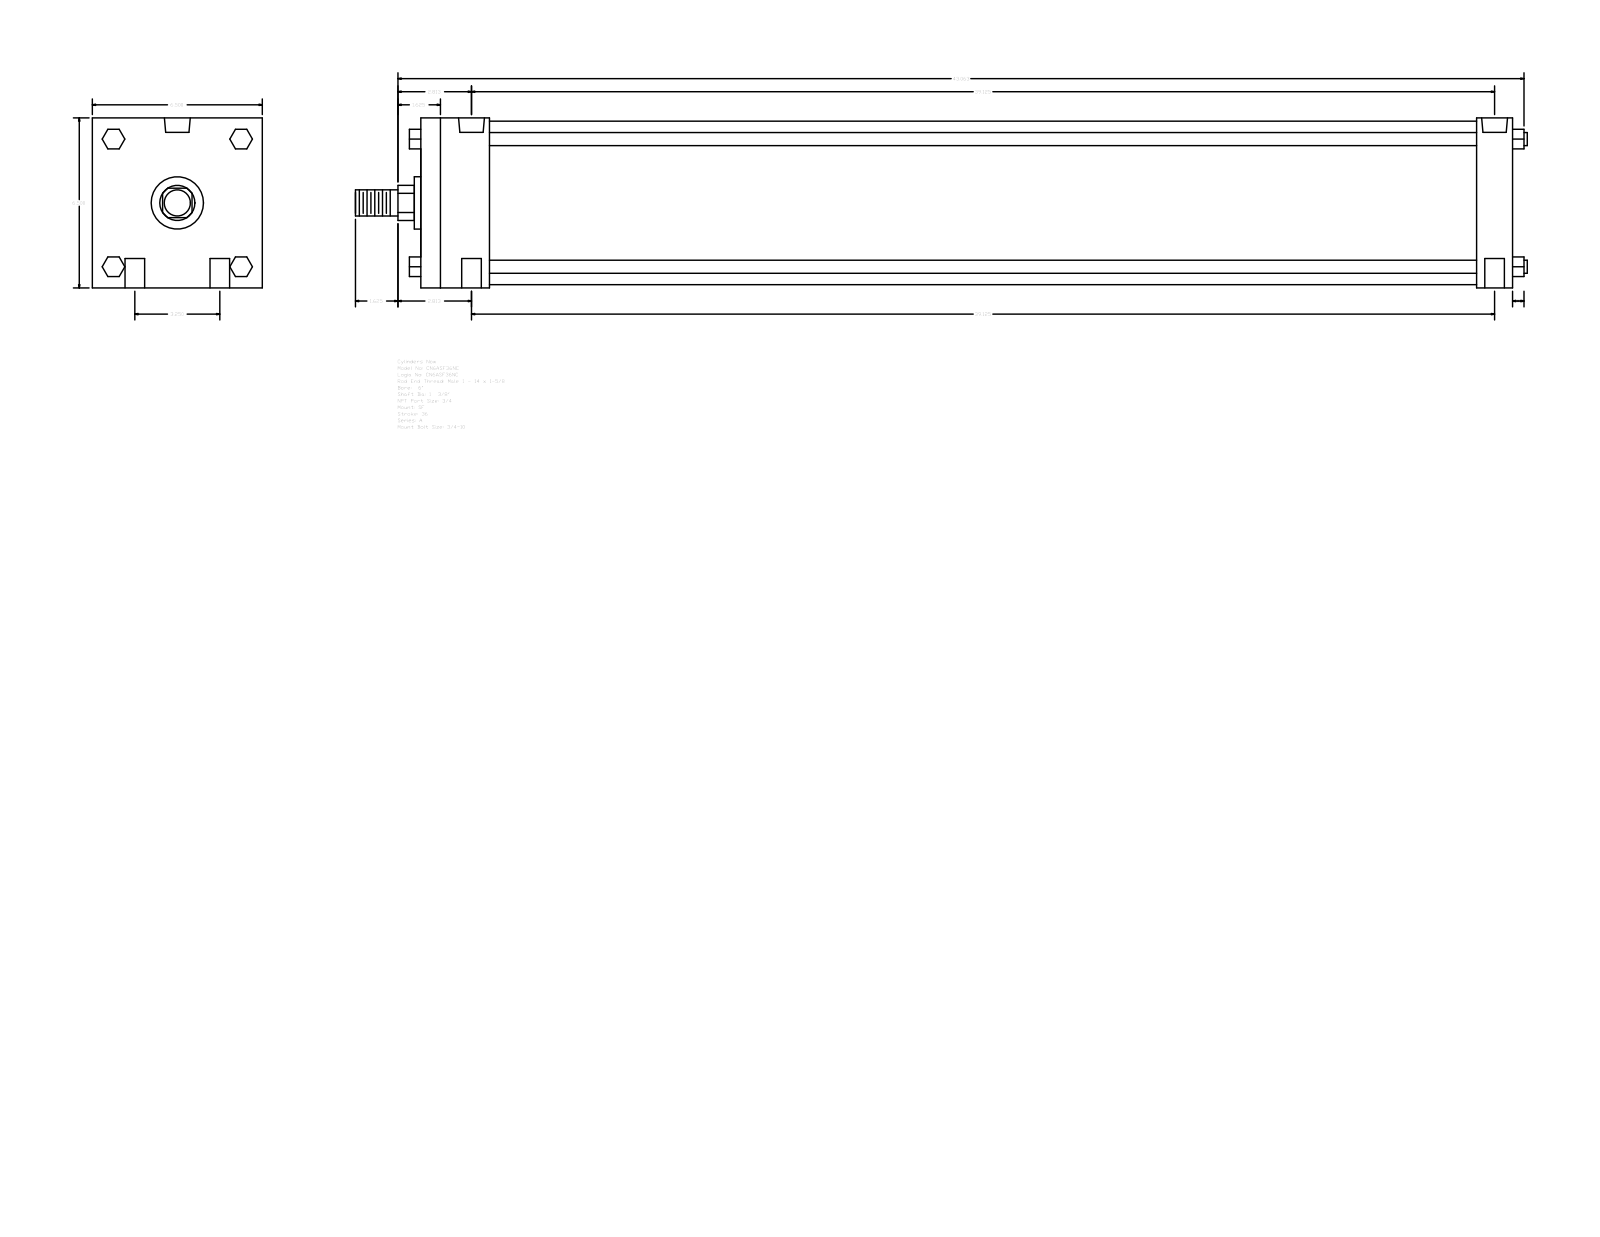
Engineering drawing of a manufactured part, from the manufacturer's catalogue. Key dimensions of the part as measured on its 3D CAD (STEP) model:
Part name (STEP PRODUCT): A_SF__0600_1.375
STEP written by: GSSL Pune (CONFIG_CONTROL_DESIGN)
Units: millimetres
Bodies: 0 solids, 124 faces (94 planar, 30 cylindrical, 0 other)
Overall size (bounding box): 1138.24 × 165.1 × 165.1
Round holes (diameter × count): ⌀19.05 ×4, ⌀15.08 ×2, ⌀25.12 ×2
Round bosses / shafts (diameter × count): ⌀12.7 ×4, ⌀158.75 ×1, ⌀50.8 ×1, ⌀34.92 ×1, ⌀25.4 ×1
Partial cylindrical surfaces — rounded edges, fillets, slot ends (radius × count): R17.06 ×1
Main face-to-face distances: 165.1, 1060.44, 1025.52, 34.92, 66.67, 958.85, 993.77, 19.05, 61.97, 107.34
Hole centre spacings: 41.27, 994.63, 993.77, 82.54, 997.19, 982.65
